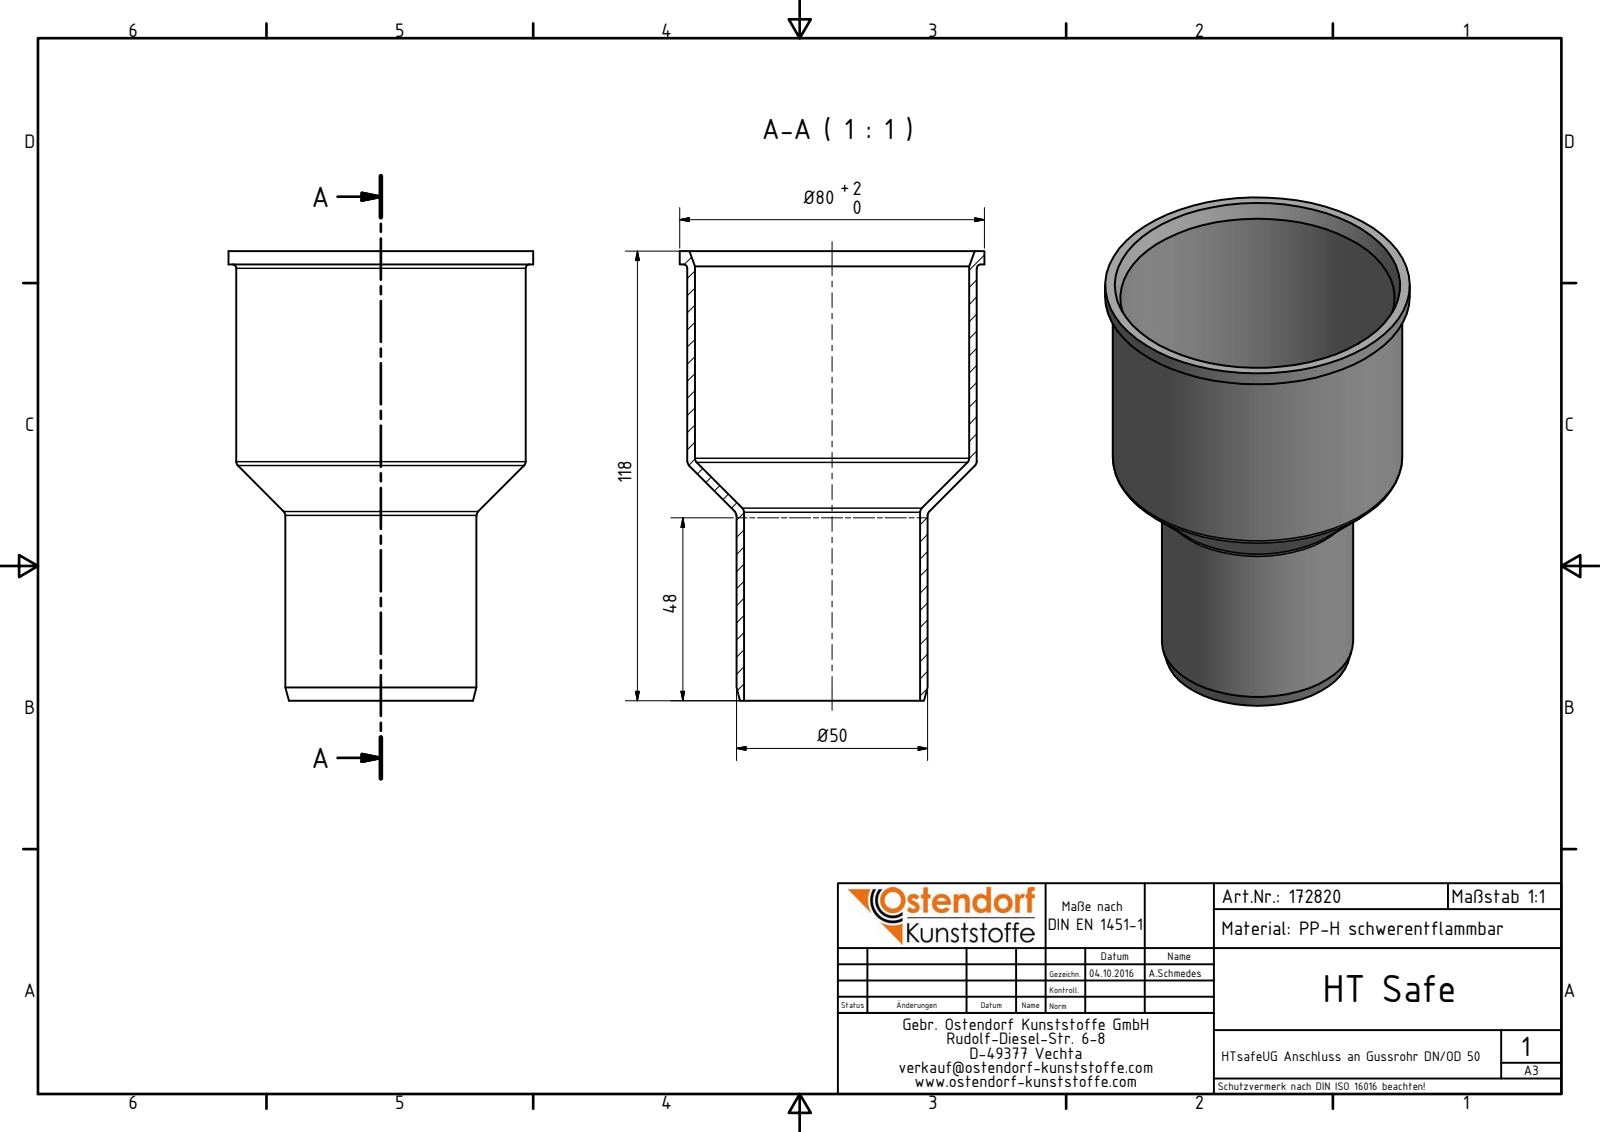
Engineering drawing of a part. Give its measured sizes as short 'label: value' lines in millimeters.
name: 172820 HTsafeUG DN_OD 50
written by: Autodesk Inventor 2016 (AUTOMOTIVE_DESIGN)
unit: mm
bodies: 1 solid, 17 faces (3 planar, 5 cylindrical, 9 other)
size: 118 × 80 × 80
volume: 48 660 mm³; area: 49 062 mm²
holes: 1× ⌀46.2, 1× ⌀72
bosses: 1× ⌀80, 1× ⌀76, 1× ⌀50.2
face distances: 3.5, 114.5, 118
